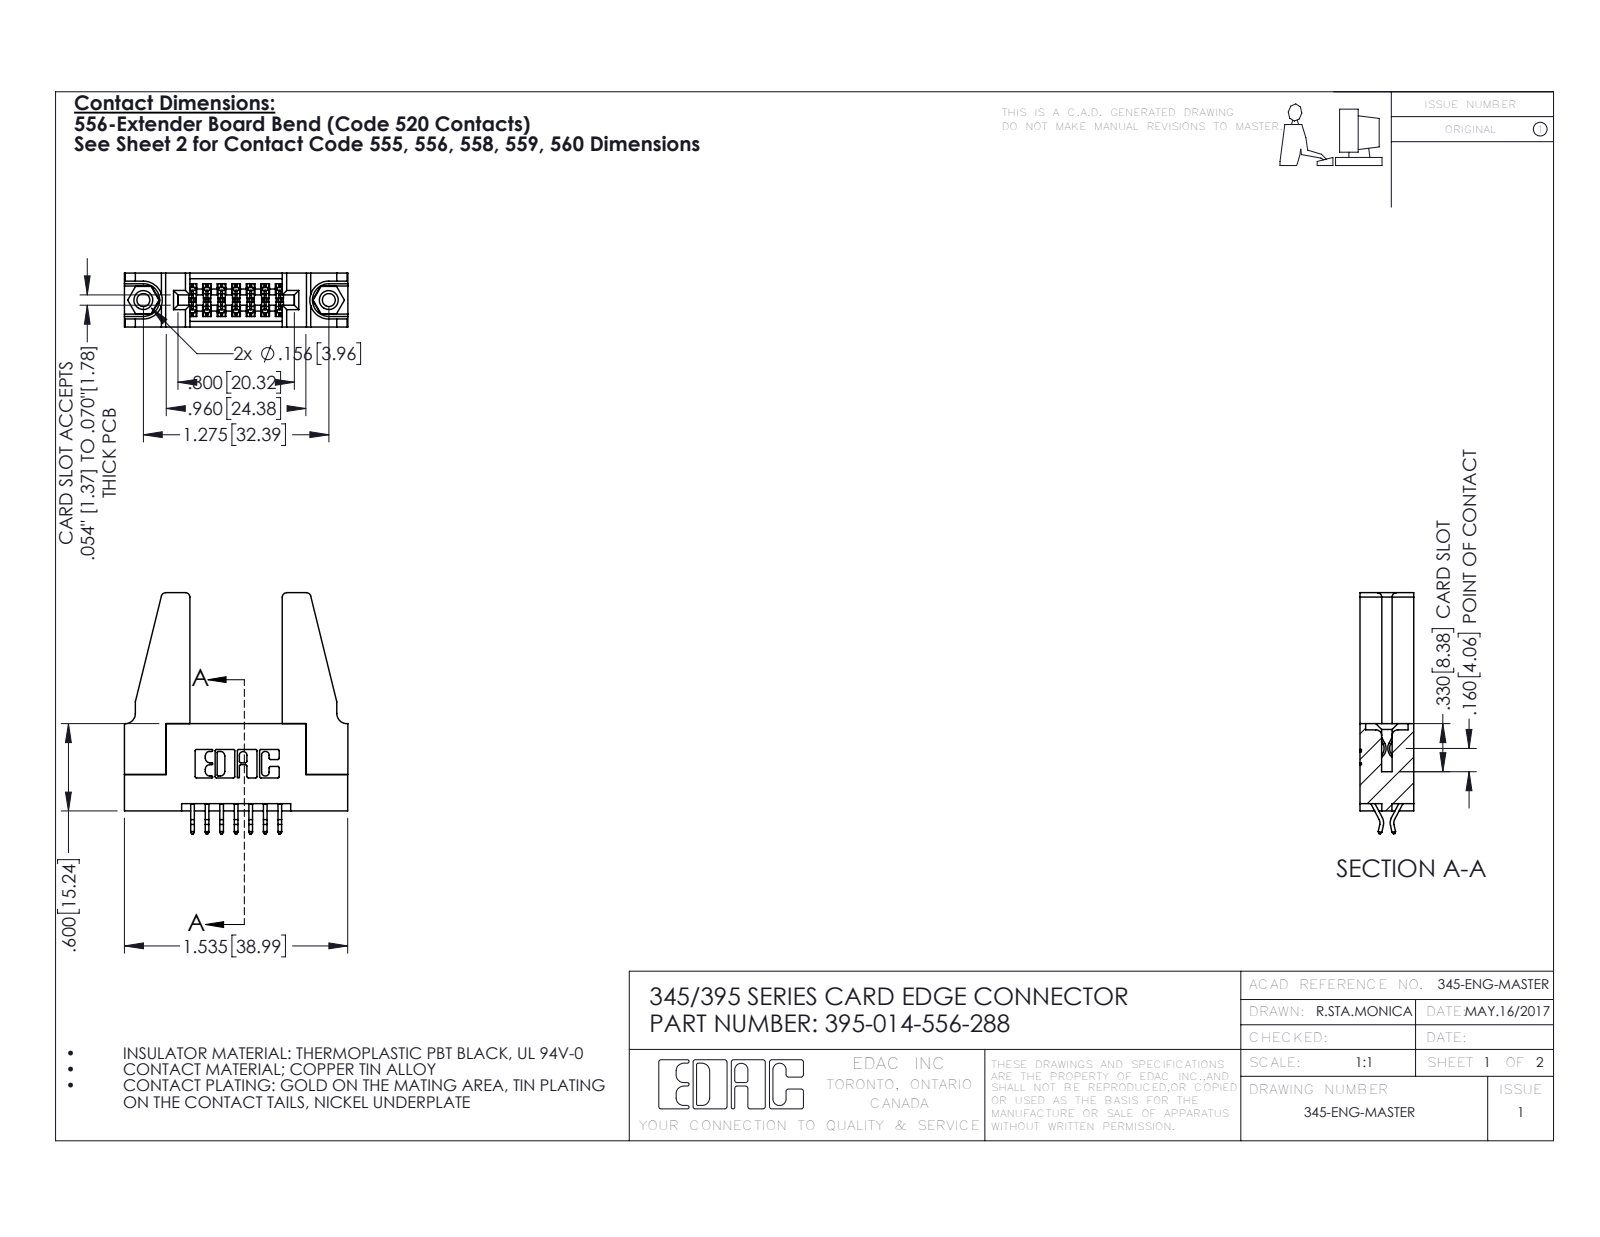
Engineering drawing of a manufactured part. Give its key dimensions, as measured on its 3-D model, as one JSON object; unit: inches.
{"part_name": "345-250-001_345-250-001-102; 345 Part_Flush Mounting Lugs - 0.156 Dia-TH; 345-292-001_556 Tail; 395-014-556-288 (+1 more)", "step_written_by": "SolidWorks 2016 (CONFIG_CONTROL_DESIGN)", "units": "inches", "bodies": {"solids": 19, "faces": 1034, "planar": 670, "cylindrical": 348, "other": 16}, "overall_size": [1.657, 1.536, 0.37], "volume_in3": 0.41, "surface_area_in2": 11.71, "round_holes": [[0.089, 2], [0.125, 2], [0.156, 2], [0.064, 1]], "round_bosses_or_shafts": [[0.155, 2]], "partial_cylinders_radius": [[0.01, 22], [0.006, 21], [0.03, 8], [0.007, 6], [0.031, 6], [0.026, 3], [0.01, 2], [0.014, 2]], "face_to_face_distances": [0.37, 0.072, 0.298, 0.2, 0.025, 0.225, 0.148, 0.15, 0.25, 0.6], "hole_center_spacings": [0.27, 1.045, 1.275]}
